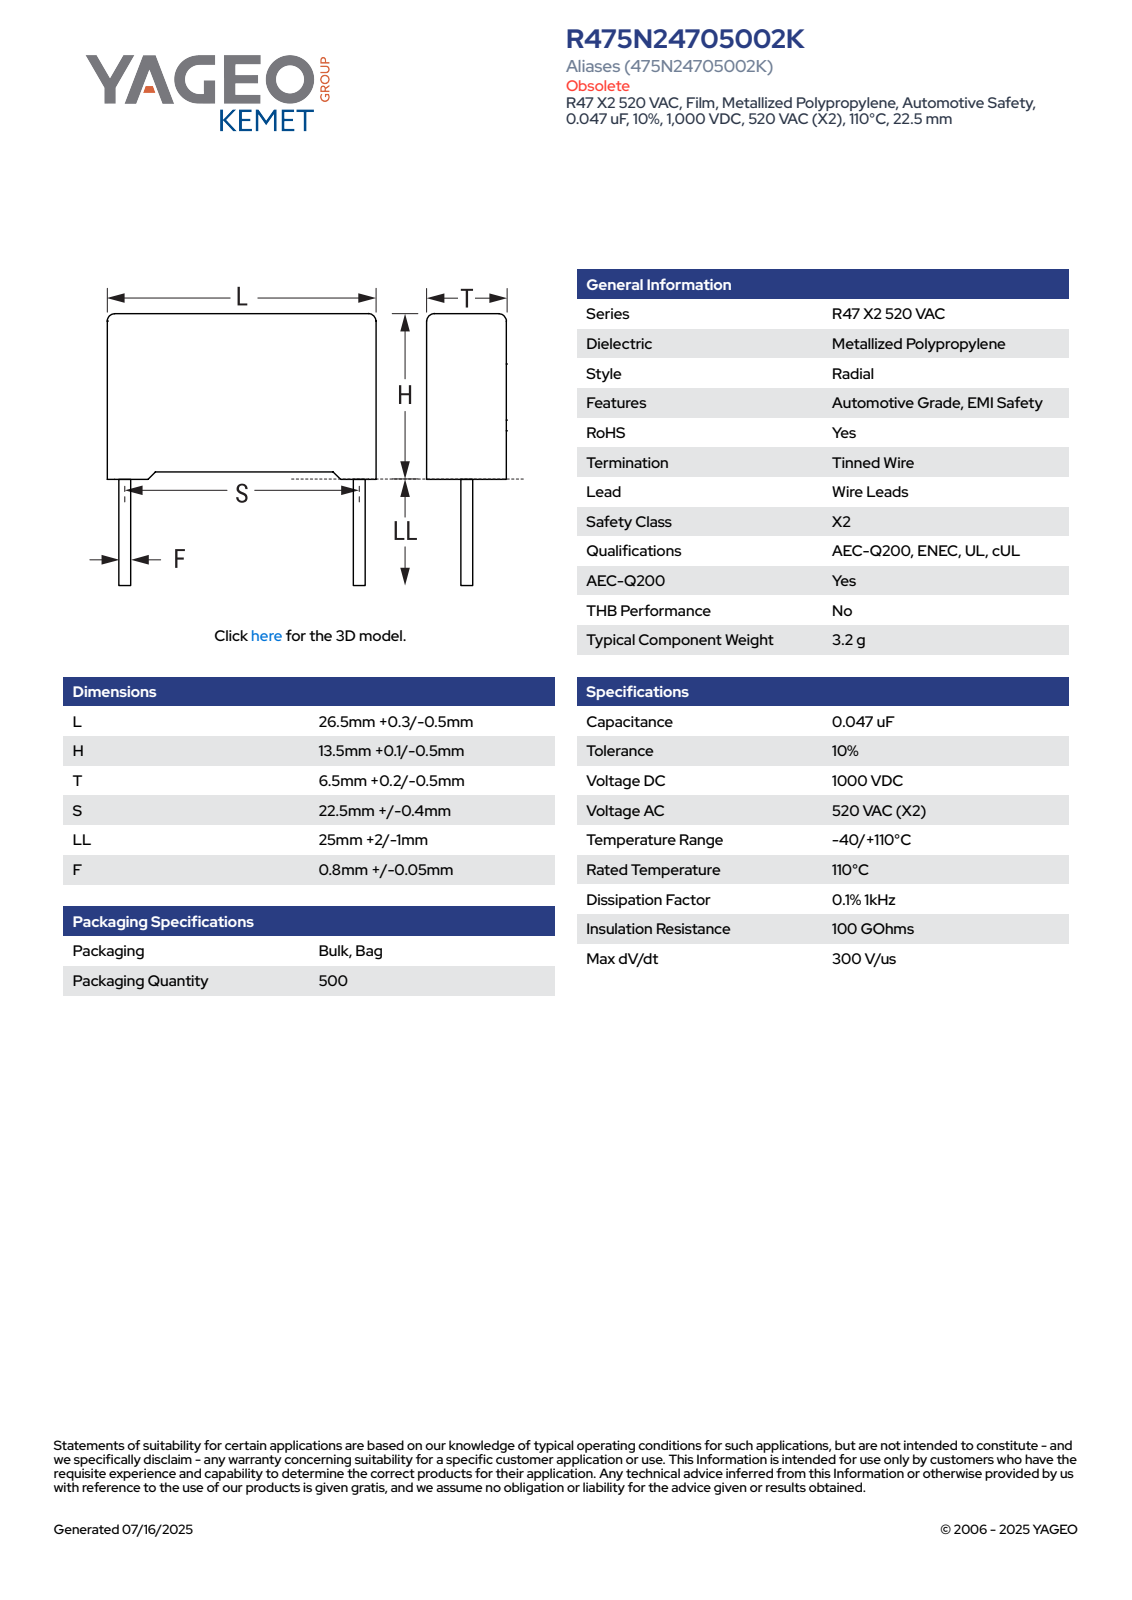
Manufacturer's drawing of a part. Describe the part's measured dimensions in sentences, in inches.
The part is named "CFR_RB2_26.5X13.5X6.5_L26.8H13.6T6.7S22.5LL27F0.85". Its 3-D file was written by "SolidWorks 2021 (AUTOMOTIVE_DESIGN)". It is 4 solids with 85 faces: 77 planar, 8 cylindrical and 0 other. Overall it measures 1.598 by 1.055 by 0.264 inches. Its volume is 0.144 cubic inches and its surface area 2.275 square inches. Round bosses or shafts: 2 of diameter 0.033. Partial cylindrical surfaces (rounded edges, fillets, slot ends): 4 of radius 0.02. The main face-to-face distances are 0.264, 0.506, 1.055, 0.517, 0.035, 0.03, 0.019, 0.535, 0.229, 0.264.
